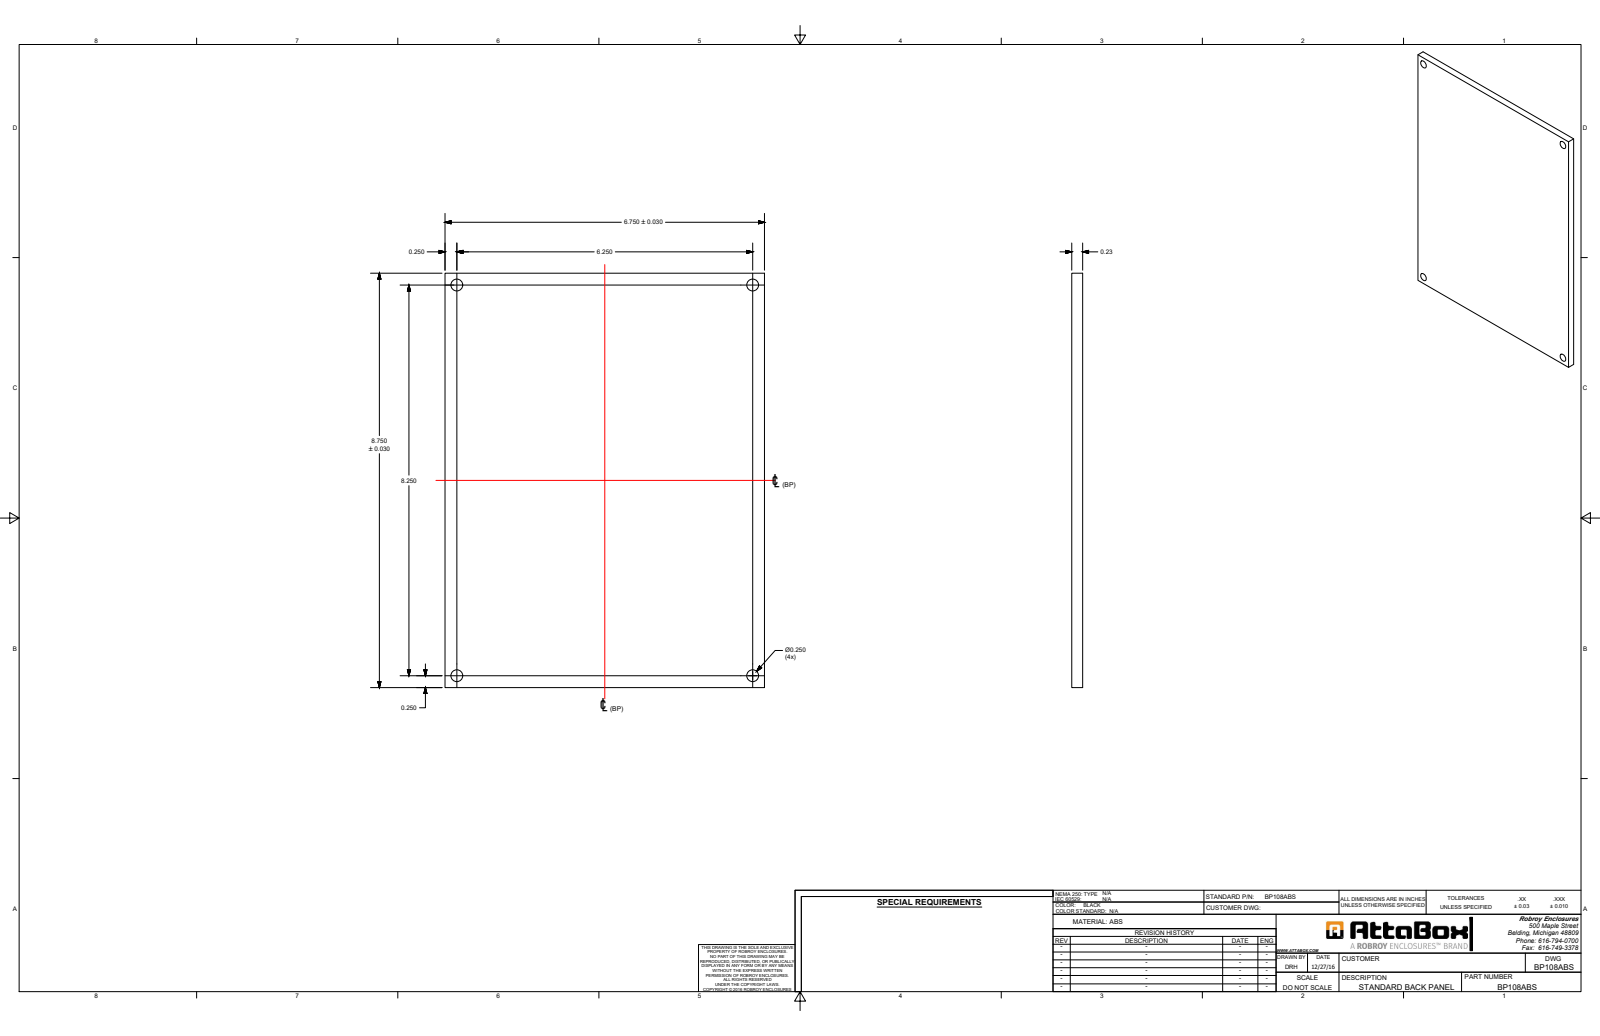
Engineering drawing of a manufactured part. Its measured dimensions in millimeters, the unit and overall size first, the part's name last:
Units: millimetres
Overall size (bounding box): 222.3 × 171.5 × 5.8
Round holes (diameter × count): ⌀6.4 ×4
Main face-to-face distances: 5.8, 171.5, 222.3
Hole centre spacings: 158.8, 209.6, 262.9
Volume: 221 900 mm³ · Surface area: 81 030 mm²
Bodies: 1 solid, 10 faces (6 planar, 4 cylindrical, 0 other)
Part name (STEP PRODUCT): BP108ABS_Default
STEP written by: SolidWorks 2023 (CONFIG_CONTROL_DESIGN)
